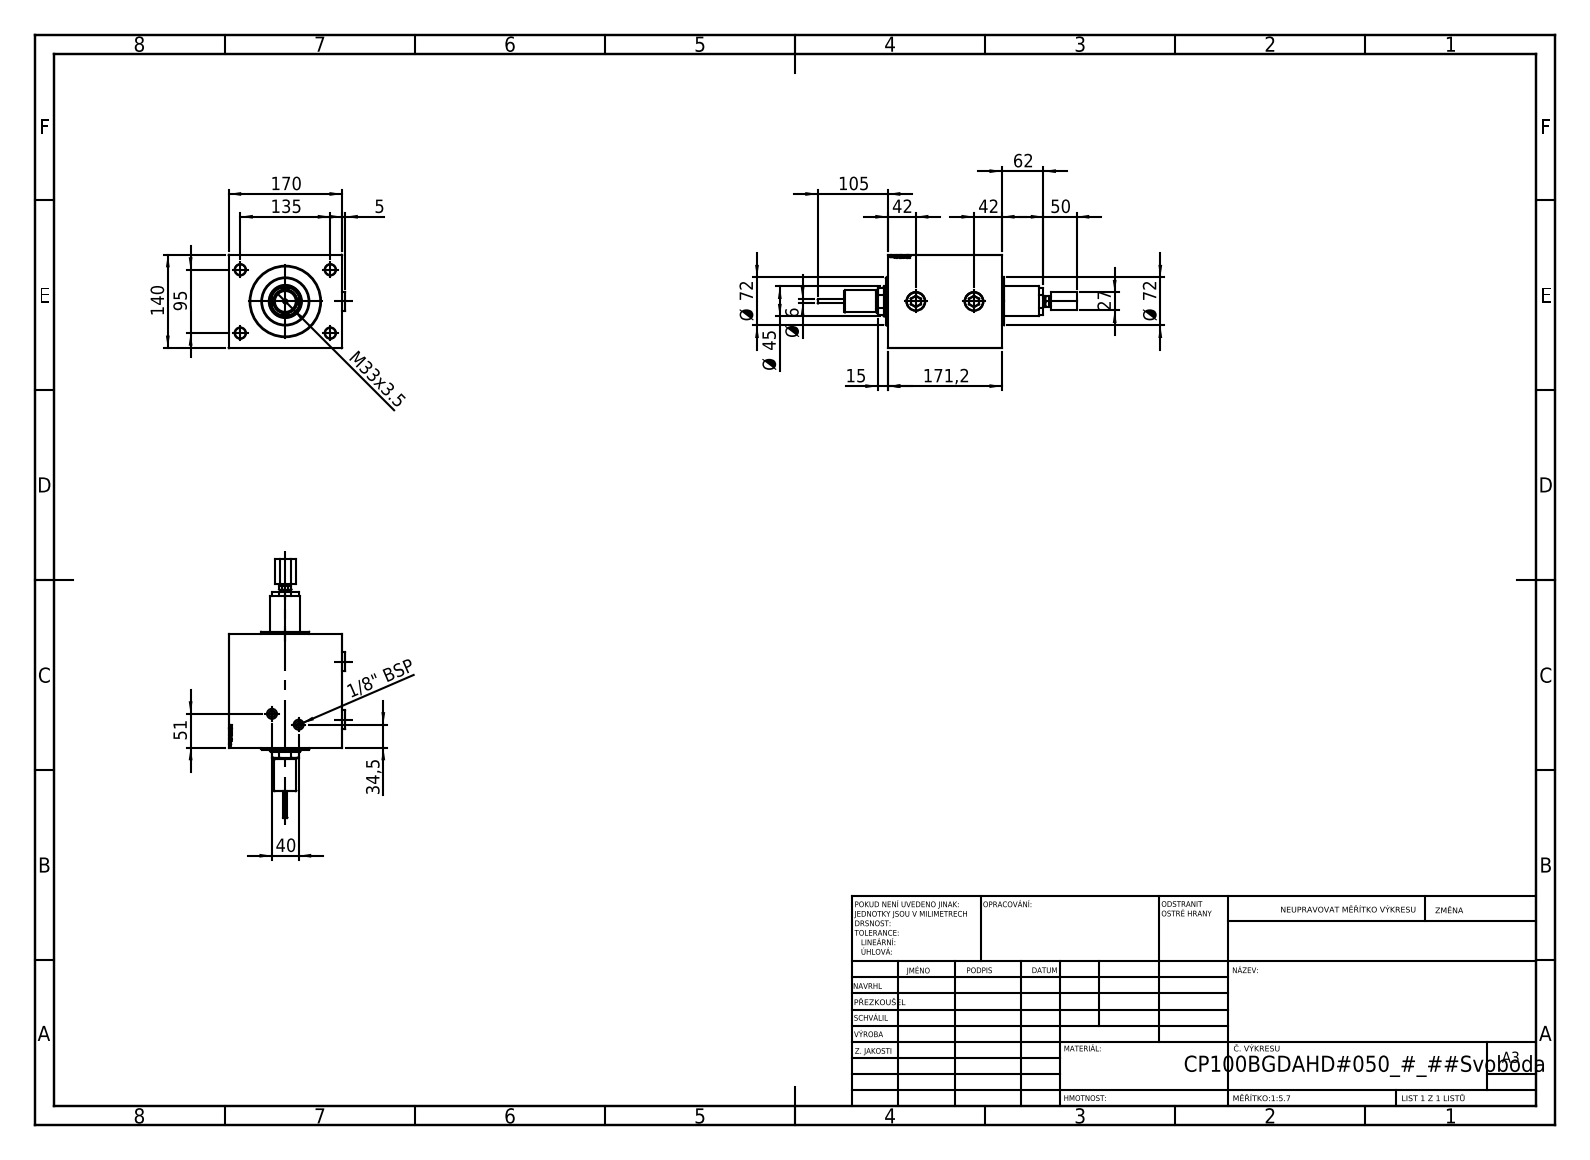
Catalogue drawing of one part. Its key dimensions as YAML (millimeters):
part_name: "V450DCP_B_Body; V450CP_MALE_METRIC; V450DCP_VC_B; V450DCP_B_VCP (+2 more)"
step_written_by: "SolidWorks 2019 (CONFIG_CONTROL_DESIGN)"
units: millimeters
bodies: {solids: 7, faces: 1040, planar: 472, cylindrical: 114, other: 454}
overall_size: [388.2, 174.9, 140]
volume: 3857000
surface_area: 351146
round_holes:
  - {diameter: 16, count: 4}
  - {diameter: 8.5, count: 3}
  - {diameter: 20.96, count: 3}
  - {diameter: 28, count: 3}
  - {diameter: 4, count: 2}
  - {diameter: 9.73, count: 2}
  - {diameter: 15, count: 2}
  - {diameter: 3, count: 1}
  - {diameter: 6, count: 1}
  - {diameter: 31.5, count: 1}
  - {diameter: 45, count: 1}
  - {diameter: 48.5, count: 1}
round_bosses_or_shafts:
  - {diameter: 72, count: 1}
  - {diameter: 33, count: 1}
  - {diameter: 31, count: 1}
  - {diameter: 13.47, count: 1}
partial_cylinders:
  - {radius: 22, count: 1}
face_to_face_distances: [140, 170, 171.2, 26, 145.2, 50, 106, 80, 65.2, 105]
hole_center_spacings: [82.54, 95, 135, 165.08, 11, 43.19, 87.2, 98.2]
